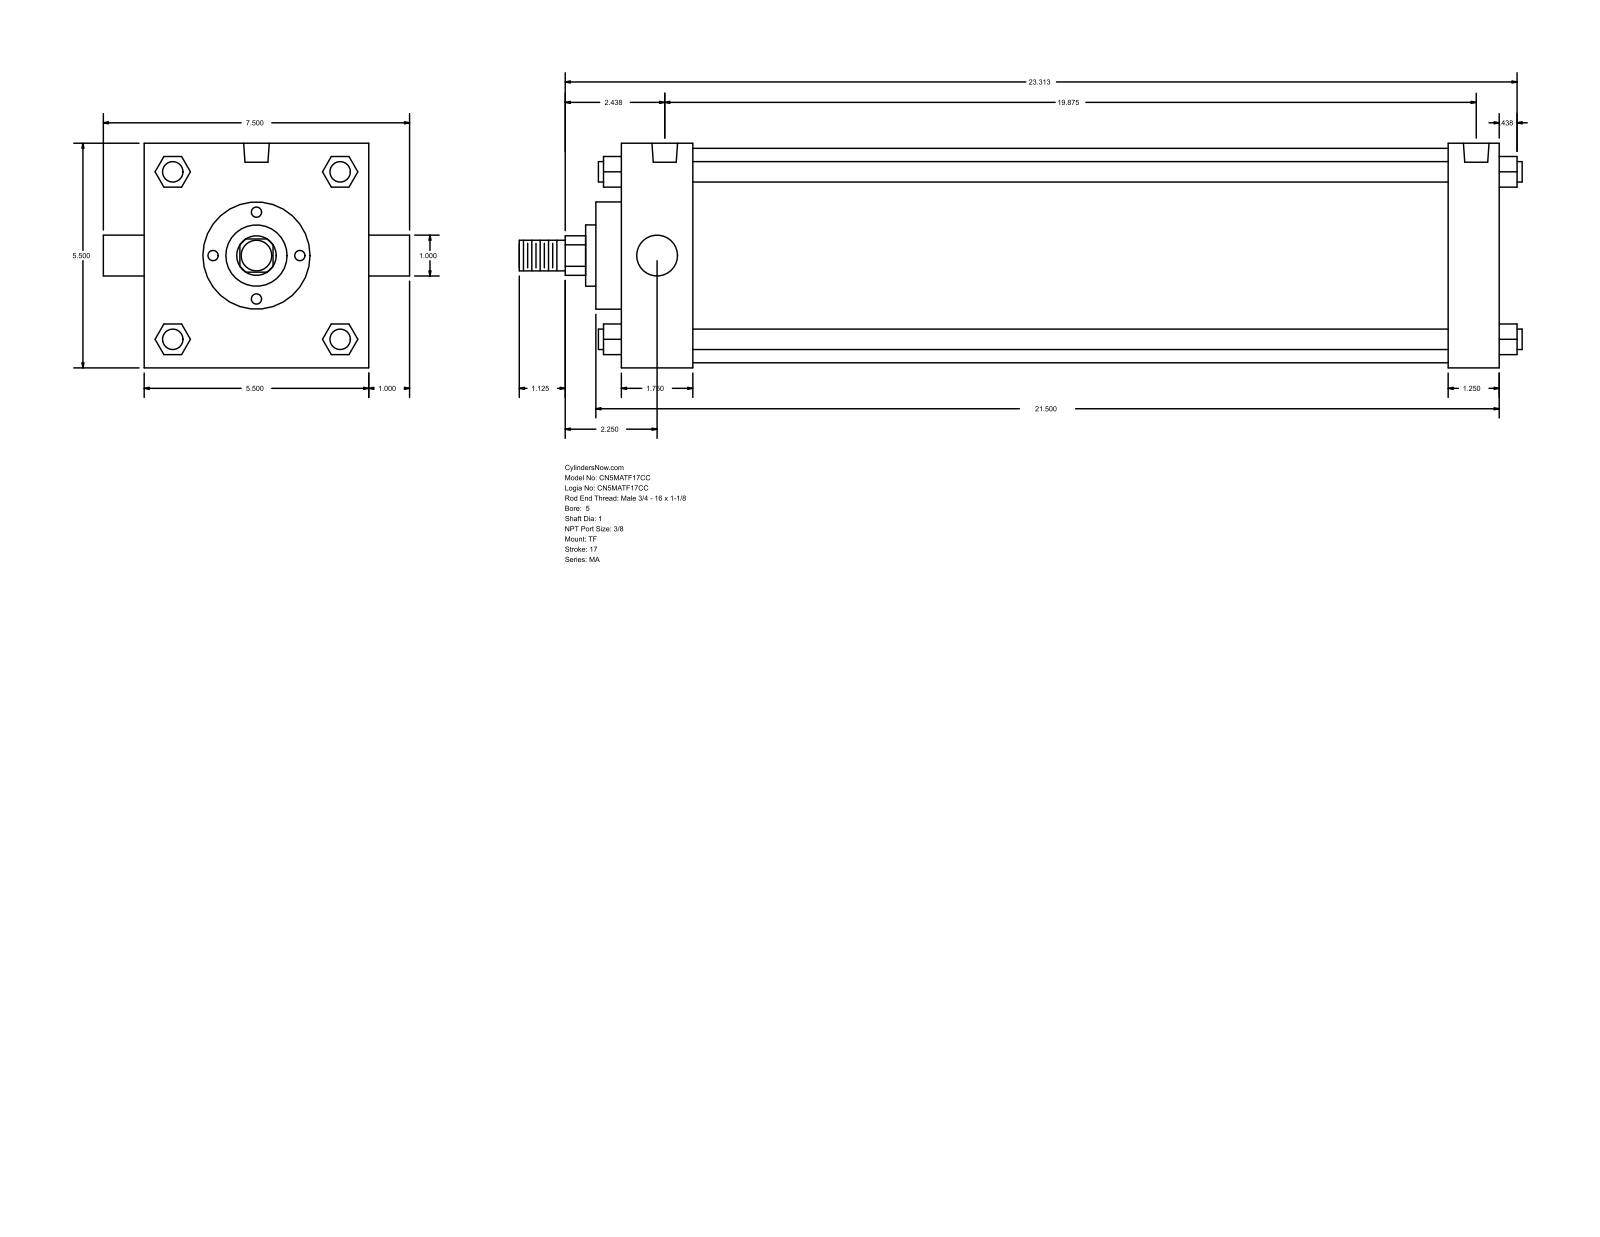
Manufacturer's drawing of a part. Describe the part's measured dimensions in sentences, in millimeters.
The part is named "MA_TF__0500_1". Its 3-D file was written by "GSSL Pune (CONFIG_CONTROL_DESIGN)". It is 0 solids with 122 faces: 93 planar, 29 cylindrical and 0 other. Overall it measures 623.89 by 190.5 by 139.7 millimeters. Round holes: 3 of diameter 11.11, 2 of diameter 15.93. Round bosses or shafts: 4 of diameter 12.7, 2 of diameter 25.4, 1 of diameter 133.35, 1 of diameter 66.67, 1 of diameter 38.1, 1 of diameter 19.05. Partial cylindrical surfaces (rounded edges, fillets, slot ends): 1 of radius 12.29. The main face-to-face distances are 139.7, 546.1, 514.35, 31.75, 44.46, 469.89, 501.64, 15.87, 60.33, 530.22. The hole center spacings are 4.76, 500.07, 495.31, 504.83.
